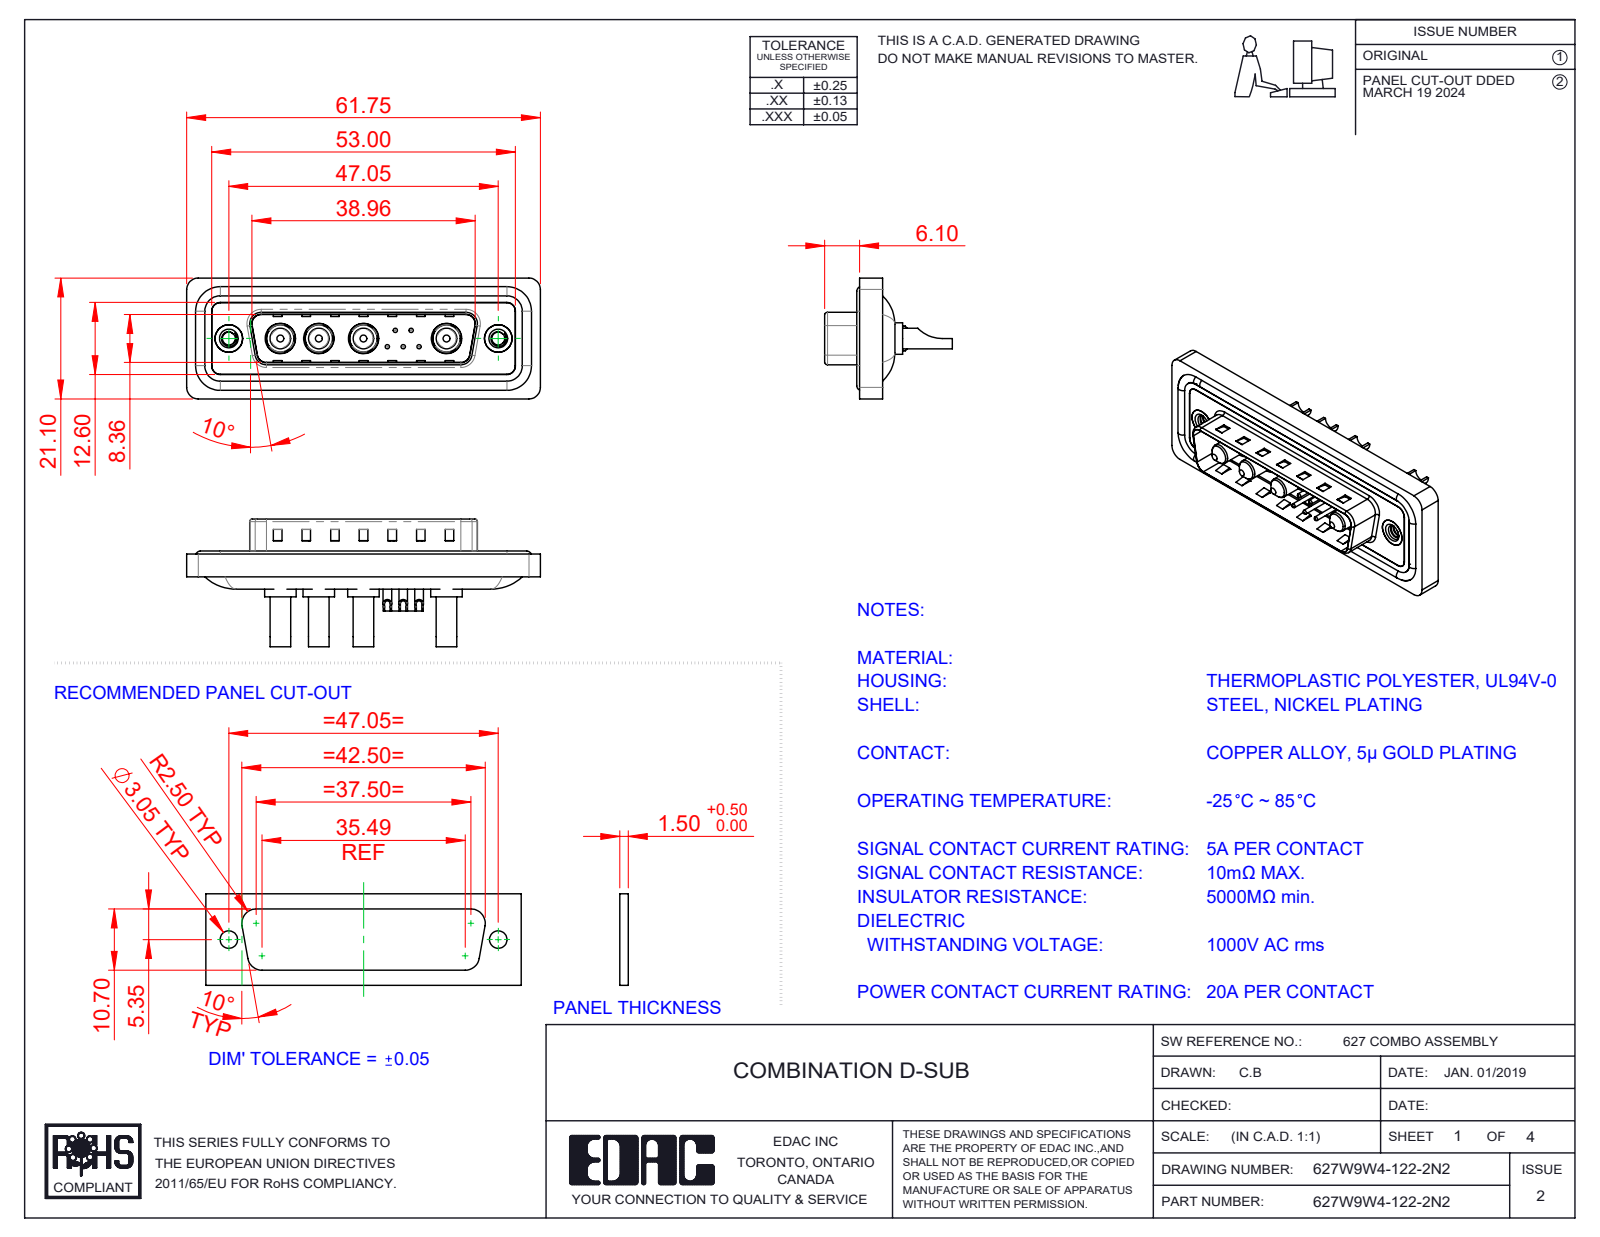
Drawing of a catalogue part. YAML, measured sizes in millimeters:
part_name: "627Combo Waterproof Housing_25 Contacts; 627Combo Contact Row 1_22; 627Combo Threaded Rivet_2; 627Combo Shell Rear_25 Contacts (+5 more)"
step_written_by: "SolidWorks 2023 (CONFIG_CONTROL_DESIGN)"
units: millimeters
bodies: {solids: 20, faces: 848, planar: 306, cylindrical: 356, other: 186}
overall_size: [61.75, 22.3, 21.1]
volume: 7463
surface_area: 12205
round_holes:
  - {diameter: 0.75, count: 5}
  - {diameter: 1, count: 5}
  - {diameter: 1.6, count: 5}
  - {diameter: 2, count: 5}
  - {diameter: 2.7, count: 4}
  - {diameter: 4.85, count: 4}
  - {diameter: 5.3, count: 4}
  - {diameter: 2.26, count: 2}
  - {diameter: 4, count: 2}
  - {diameter: 4.8, count: 2}
  - {diameter: 5, count: 2}
round_bosses_or_shafts:
  - {diameter: 1.5, count: 5}
  - {diameter: 5.5, count: 4}
  - {diameter: 5.2, count: 4}
  - {diameter: 4.75, count: 4}
  - {diameter: 3.75, count: 4}
  - {diameter: 3.6, count: 4}
  - {diameter: 1.6, count: 4}
  - {diameter: 4.9, count: 2}
partial_cylinders:
  - {radius: 1.5, count: 22}
  - {radius: 2, count: 18}
  - {radius: 0.5, count: 8}
  - {radius: 1.6, count: 8}
  - {radius: 1, count: 6}
  - {radius: 0.25, count: 4}
  - {radius: 0.6, count: 4}
  - {radius: 0.65, count: 4}
face_to_face_distances: [0.4, 1.5, 1.1, 0.5, 1.6, 3.1, 2.9, 0.82, 9.58, 5.65]
hole_center_spacings: [3.16, 2.77, 5.04, 14.51, 2.78, 4.4, 4.41, 5]
